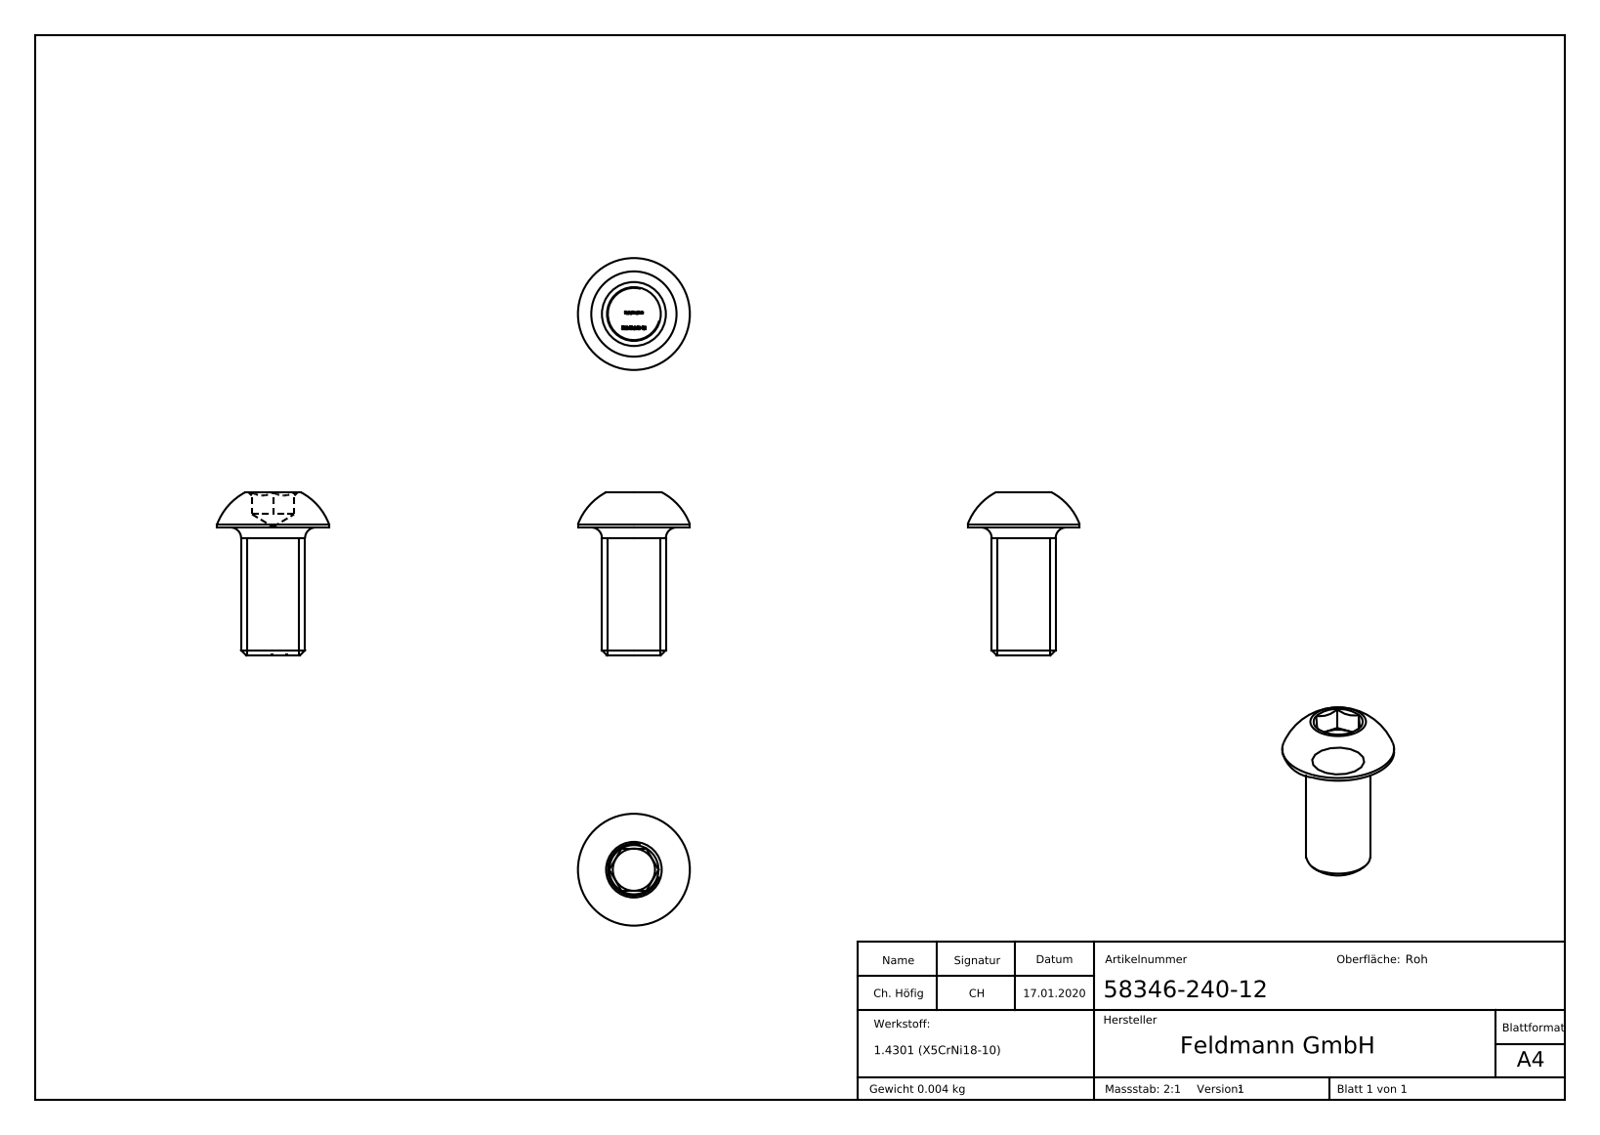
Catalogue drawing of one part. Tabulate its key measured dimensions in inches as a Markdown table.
| quantity | value |
| --- | --- |
| part name | 58346-240-12 |
| STEP written by | SolidWorks 2015 (CONFIG_CONTROL_DESIGN) |
| units | inches |
| bodies | 1 solid, 286 faces (157 planar, 2 cylindrical, 127 other) |
| overall size | 0.709 × 0.413 × 0.413 |
| volume | 0.031 in³ |
| surface area | 0.725 in² |
| round bosses / shafts (diameter × count) | 0.413 × 1, 0.236 × 1 |
| main face-to-face distances | 0.472, 0.157, 0.13, 0.602, 0.049, 0.081, 0.521, 0.598, 0.517, 0.469 |
